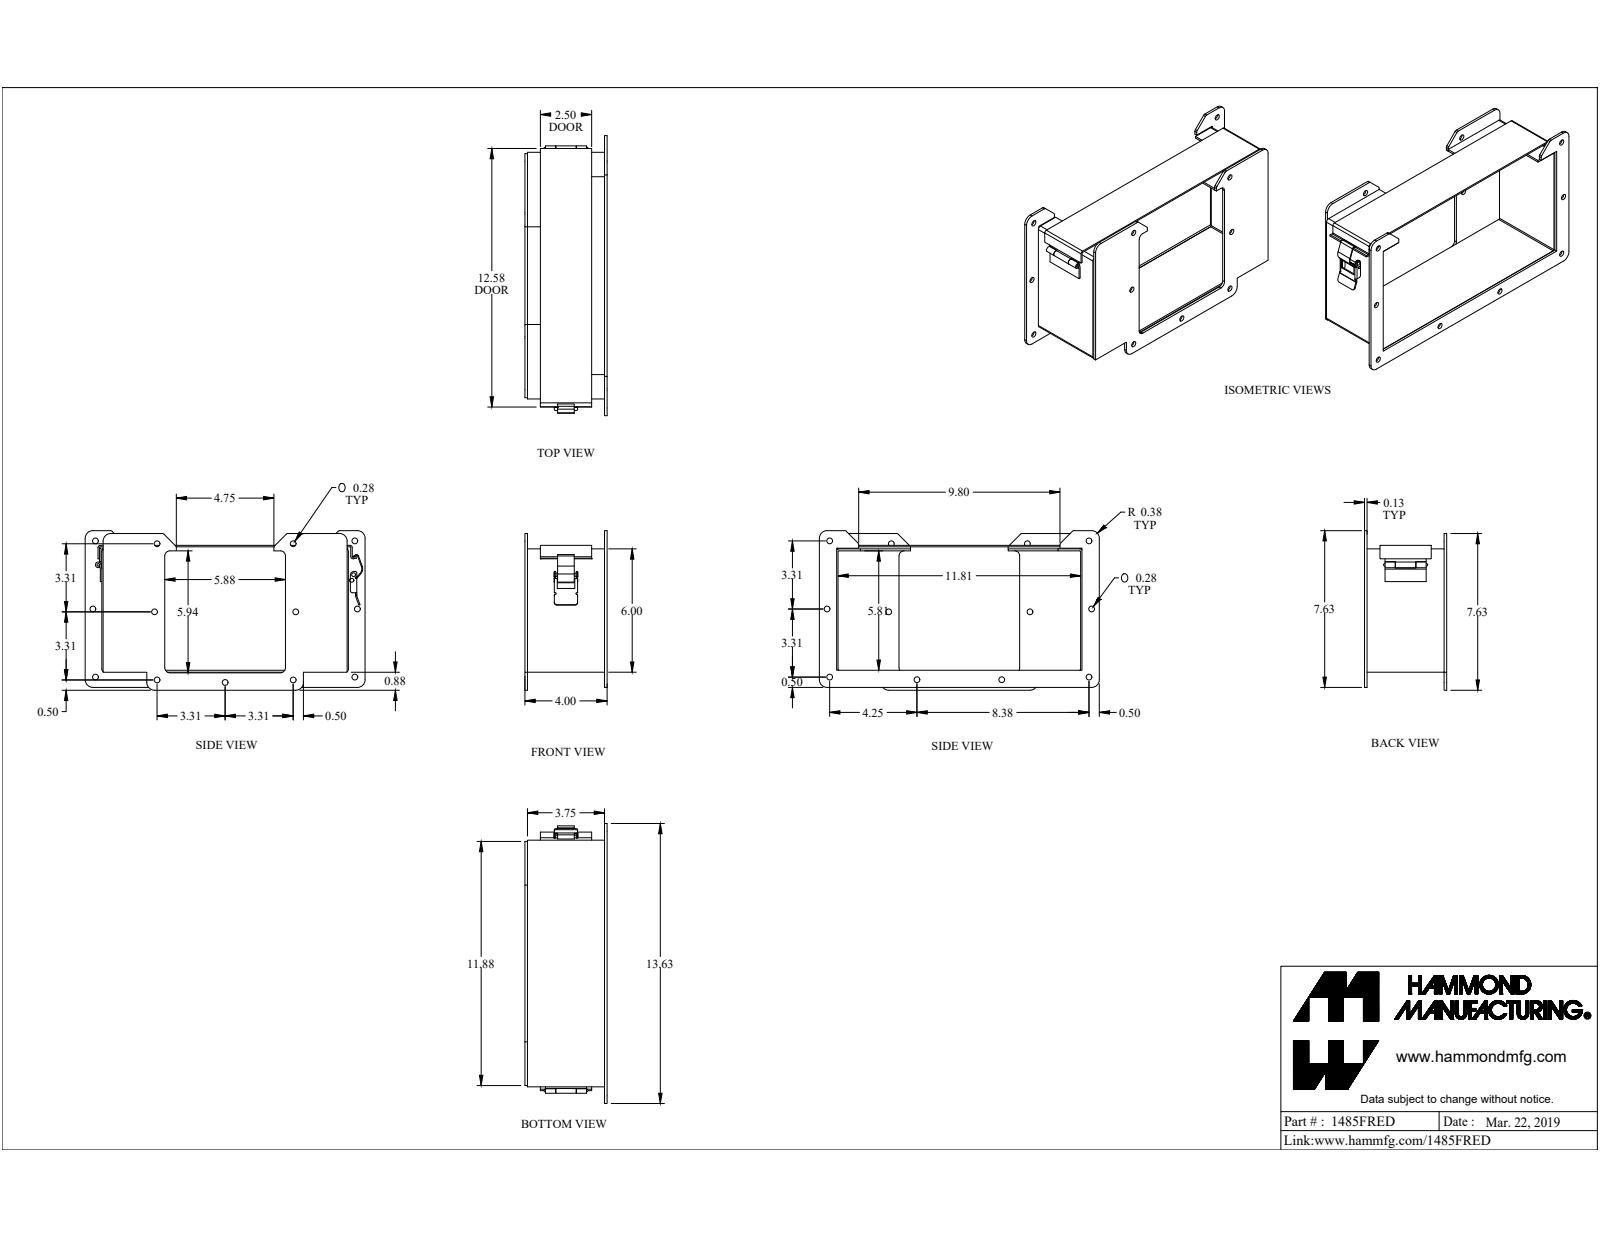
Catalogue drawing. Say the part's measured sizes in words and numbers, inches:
The part is named "1485FRED". Its 3-D file was written by "SolidWorks 2019 (CONFIG_CONTROL_DESIGN)". It is 10 solids with 260 faces: 150 planar, 108 cylindrical and 2 other. Overall it measures 13.625 by 7.763 by 4 inches. Its volume is 21.92 cubic inches and its surface area 465.9 square inches. Round holes: 15 of diameter 0.281, 1 of diameter 0.125, 1 of diameter 0.13, 1 of diameter 0.164. Round bosses or shafts: 2 of diameter 0.187, 1 of diameter 0.275, 1 of diameter 0.156, 1 of diameter 0.125, 1 of diameter 0.125. Partial cylindrical surfaces (rounded edges, fillets, slot ends): 11 of radius 0.125, 8 of radius 0.375, 7 of radius 0.016, 4 of radius 0.048, 4 of radius 0.143, 4 of radius 0.25, 3 of radius 0.035, 3 of radius 0.036. The main face-to-face distances are 0.095, 0.125, 11.905, 5.905, 0.072, 6.1, 6.172, 6.005, 6.077, 3.875. The hole center spacings are 3.315, 3.003, 7.519, 6.625, 9.626, 10.254, 10.343, 13.173.
